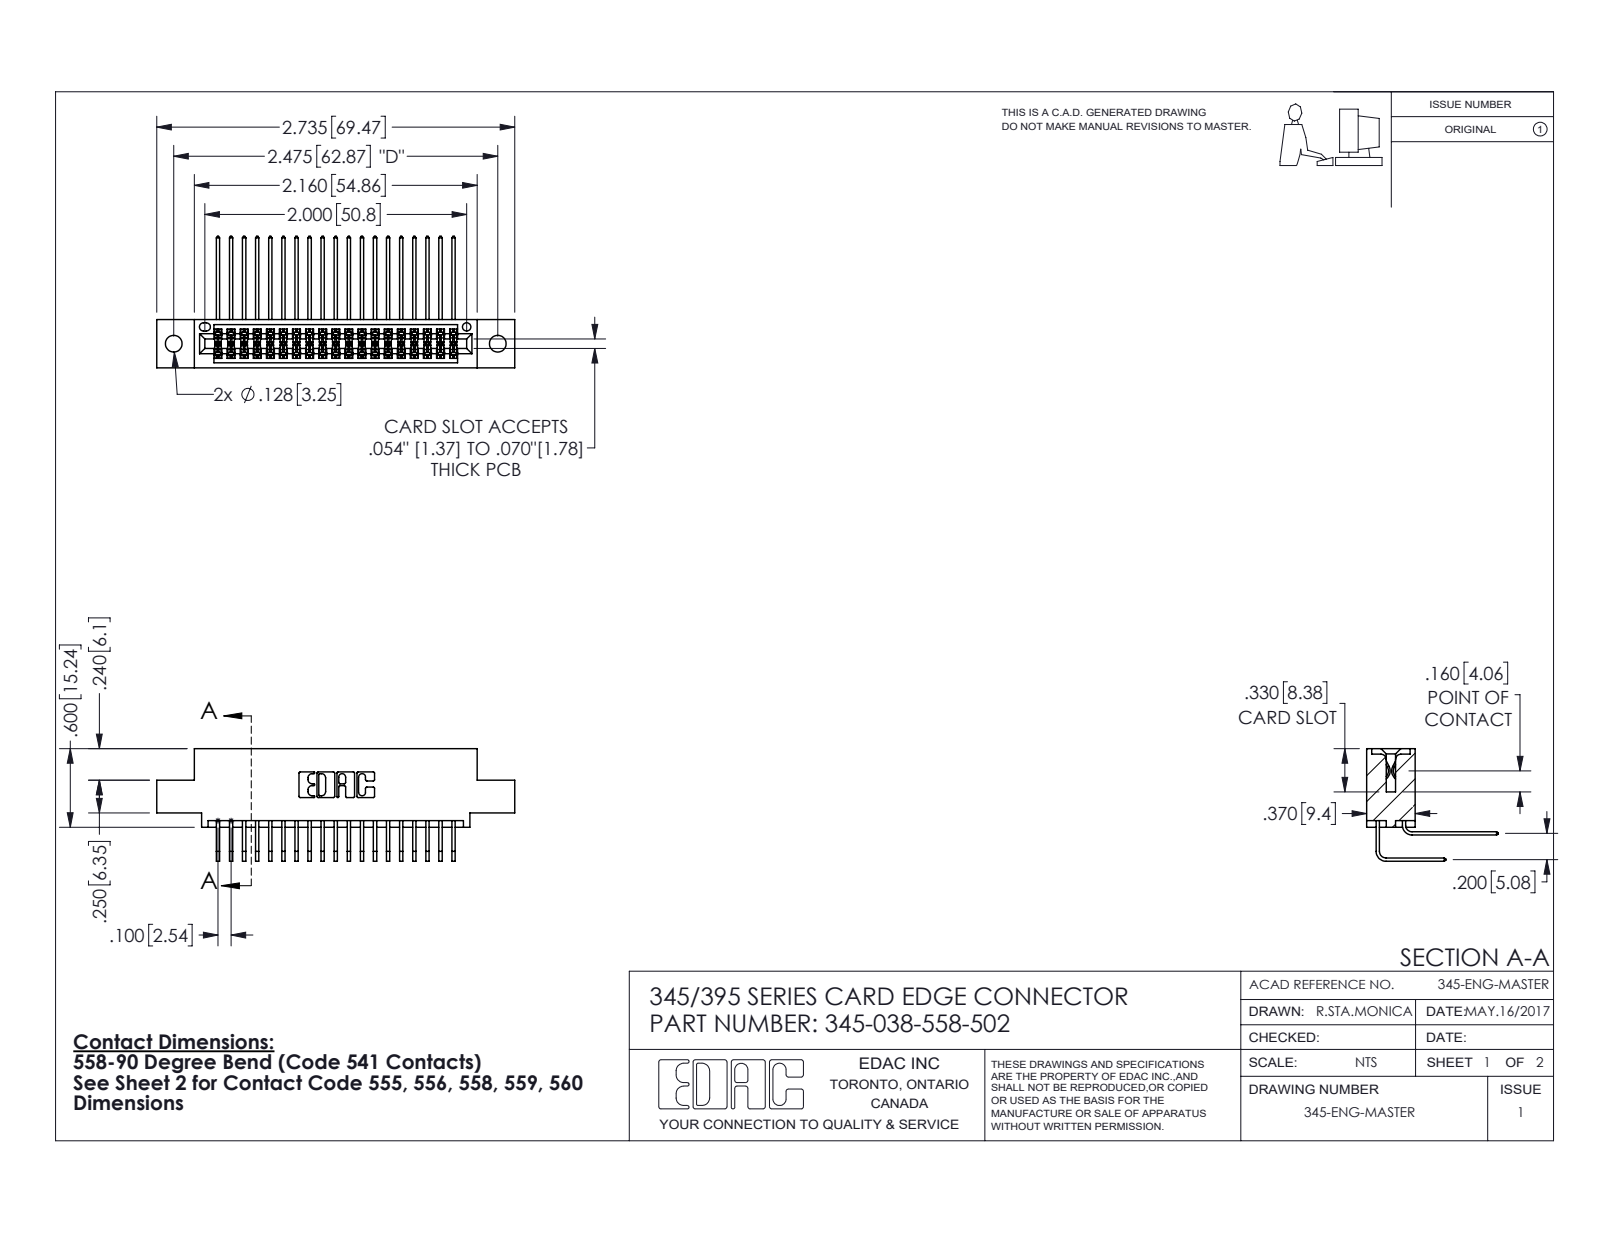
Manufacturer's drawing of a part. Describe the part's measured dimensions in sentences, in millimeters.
The part is named "345-038-558-502; 345-292-001_558 Tail - 2; 345-292-001_558 559 Tail - 1; 345 Part_0.110 Offset - 0.128 Dia". Its 3-D file was written by "SolidWorks 2016 (CONFIG_CONTROL_DESIGN)". It is 39 solids with 2106 faces: 1414 planar, 692 cylindrical and 0 other. Overall it measures 69.5 by 25.5 by 21.8 millimeters. Its volume is 6 640 cubic millimeters and its surface area 10 230 square millimeters. Round holes: 2 of diameter 3.3, 1 of diameter 1.6. Partial cylindrical surfaces (rounded edges, fillets, slot ends): 76 of radius 0.2, 22 of radius 0.3, 6 of radius 0.2, 6 of radius 0.8, 3 of radius 0.7, 2 of radius 0.4, 2 of radius 0.5, 2 of radius 0.6. The main face-to-face distances are 5.1, 1.8, 7.6, 9.4, 2.5, 6.9, 0.6, 5.7, 0.6, 4.4. The hole center spacings are 6.9, 56.9, 62.9.
